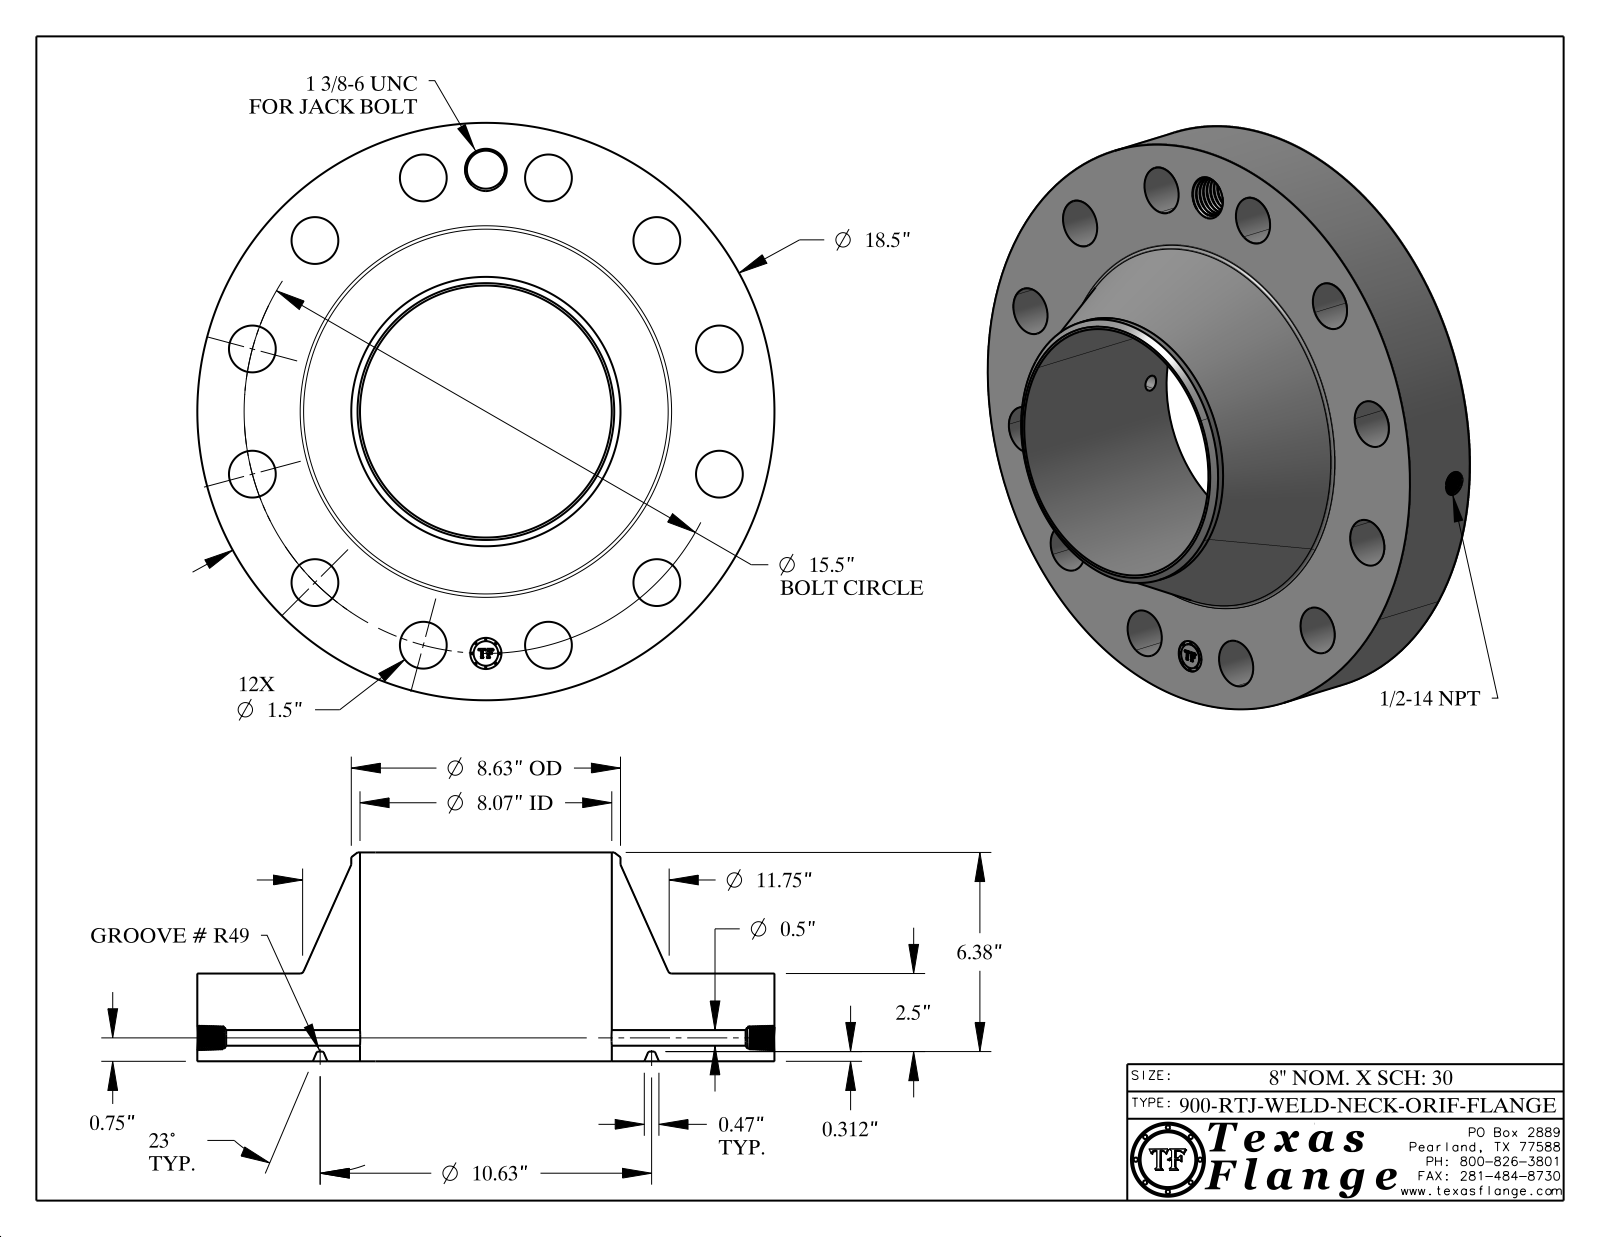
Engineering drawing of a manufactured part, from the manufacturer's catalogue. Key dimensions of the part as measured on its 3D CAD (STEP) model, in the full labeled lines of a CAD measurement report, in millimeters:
Part name (STEP PRODUCT): 900-RTJ-WELD-NECK
STEP written by: CATIA V5 STEP AP214 (AUTOMOTIVE_DESIGN)
Units: millimetres
Bodies: 1 solid, 796 faces (370 planar, 103 cylindrical, 323 other)
Overall size (bounding box): 469.9 × 469.9 × 170
Volume: 10 710 000 mm³ · Surface area: 652 300 mm²
Round holes (diameter × count): ⌀38.1 ×12, ⌀12.7 ×1, ⌀17.1 ×1, ⌀25.4 ×1, ⌀31 ×1, ⌀205 ×1
Round bosses / shafts (diameter × count): ⌀1.5 ×8, ⌀469.9 ×1, ⌀219.2 ×1, ⌀20 ×1
Main face-to-face distances: 71.4, 7.9, 63.5, 170, 162.1, 98.6, 71, 63.1, 0.4, 98.9
Hole centre spacings: 196.9, 340.9, 380.3, 101.9, 196.9, 278.4, 393.7, 51.4
